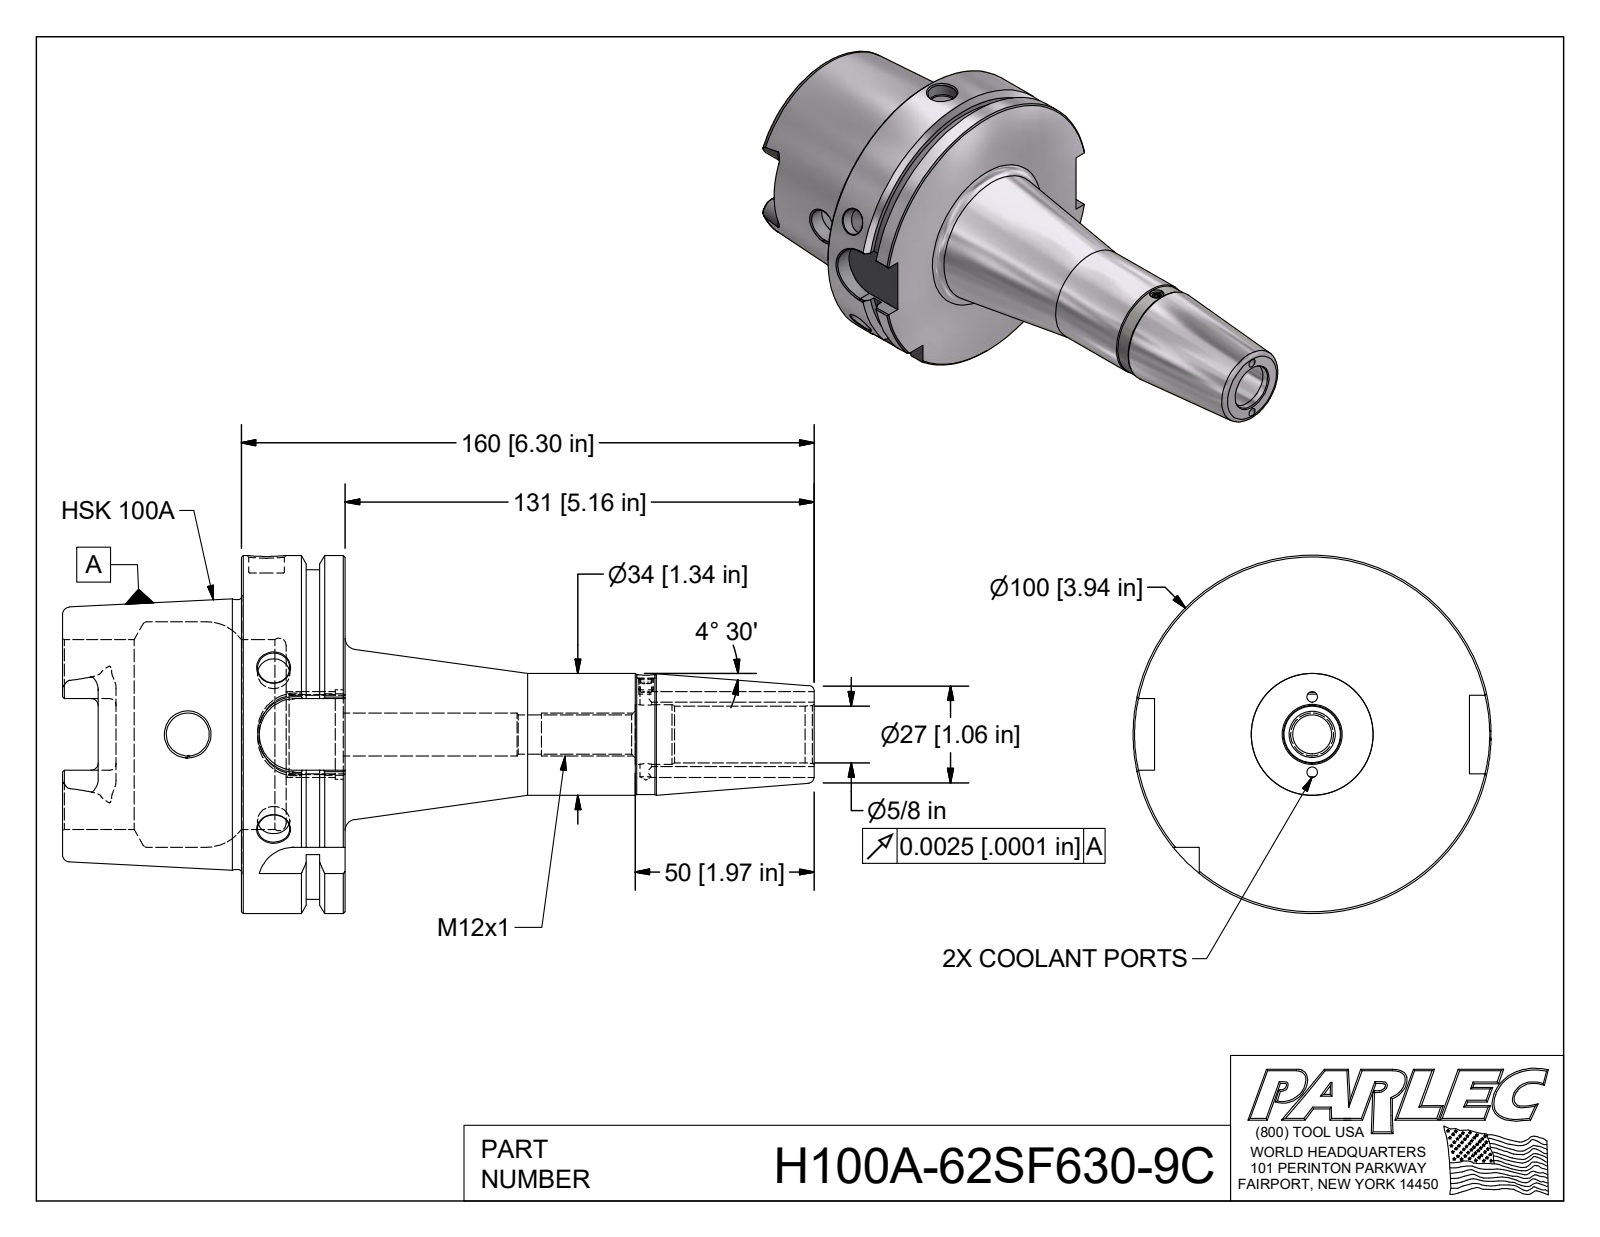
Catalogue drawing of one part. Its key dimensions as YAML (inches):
step_written_by: "Autodesk Inventor 2018 (AUTOMOTIVE_DESIGN)"
units: inches
bodies: {solids: 1, faces: 154, planar: 49, cylindrical: 43, other: 62}
overall_size: [8.268, 3.937, 3.937]
volume: 22.46
surface_area: 107.8
round_holes:
  - {diameter: 0.118, count: 2}
  - {diameter: 0.354, count: 2}
  - {diameter: 0.472, count: 2}
  - {diameter: 0.128, count: 1}
  - {diameter: 0.197, count: 1}
  - {diameter: 0.394, count: 1}
  - {diameter: 0.43, count: 1}
  - {diameter: 0.624, count: 1}
  - {diameter: 0.654, count: 1}
  - {diameter: 0.881, count: 1}
  - {diameter: 0.985, count: 1}
  - {diameter: 2.087, count: 1}
round_bosses_or_shafts:
  - {diameter: 3.937, count: 1}
  - {diameter: 3.622, count: 1}
  - {diameter: 2.967, count: 1}
  - {diameter: 1.339, count: 1}
  - {diameter: 1.319, count: 1}
partial_cylinders:
  - {radius: 0.079, count: 6}
  - {radius: 0.192, count: 4}
  - {radius: 0.394, count: 4}
face_to_face_distances: [1.142, 0.492, 0.65, 1.969, 2.461, 3.11, 3.465, 2.83, 0.861, 0.369]
hole_center_spacings: [0.413, 0.826, 4.174]
